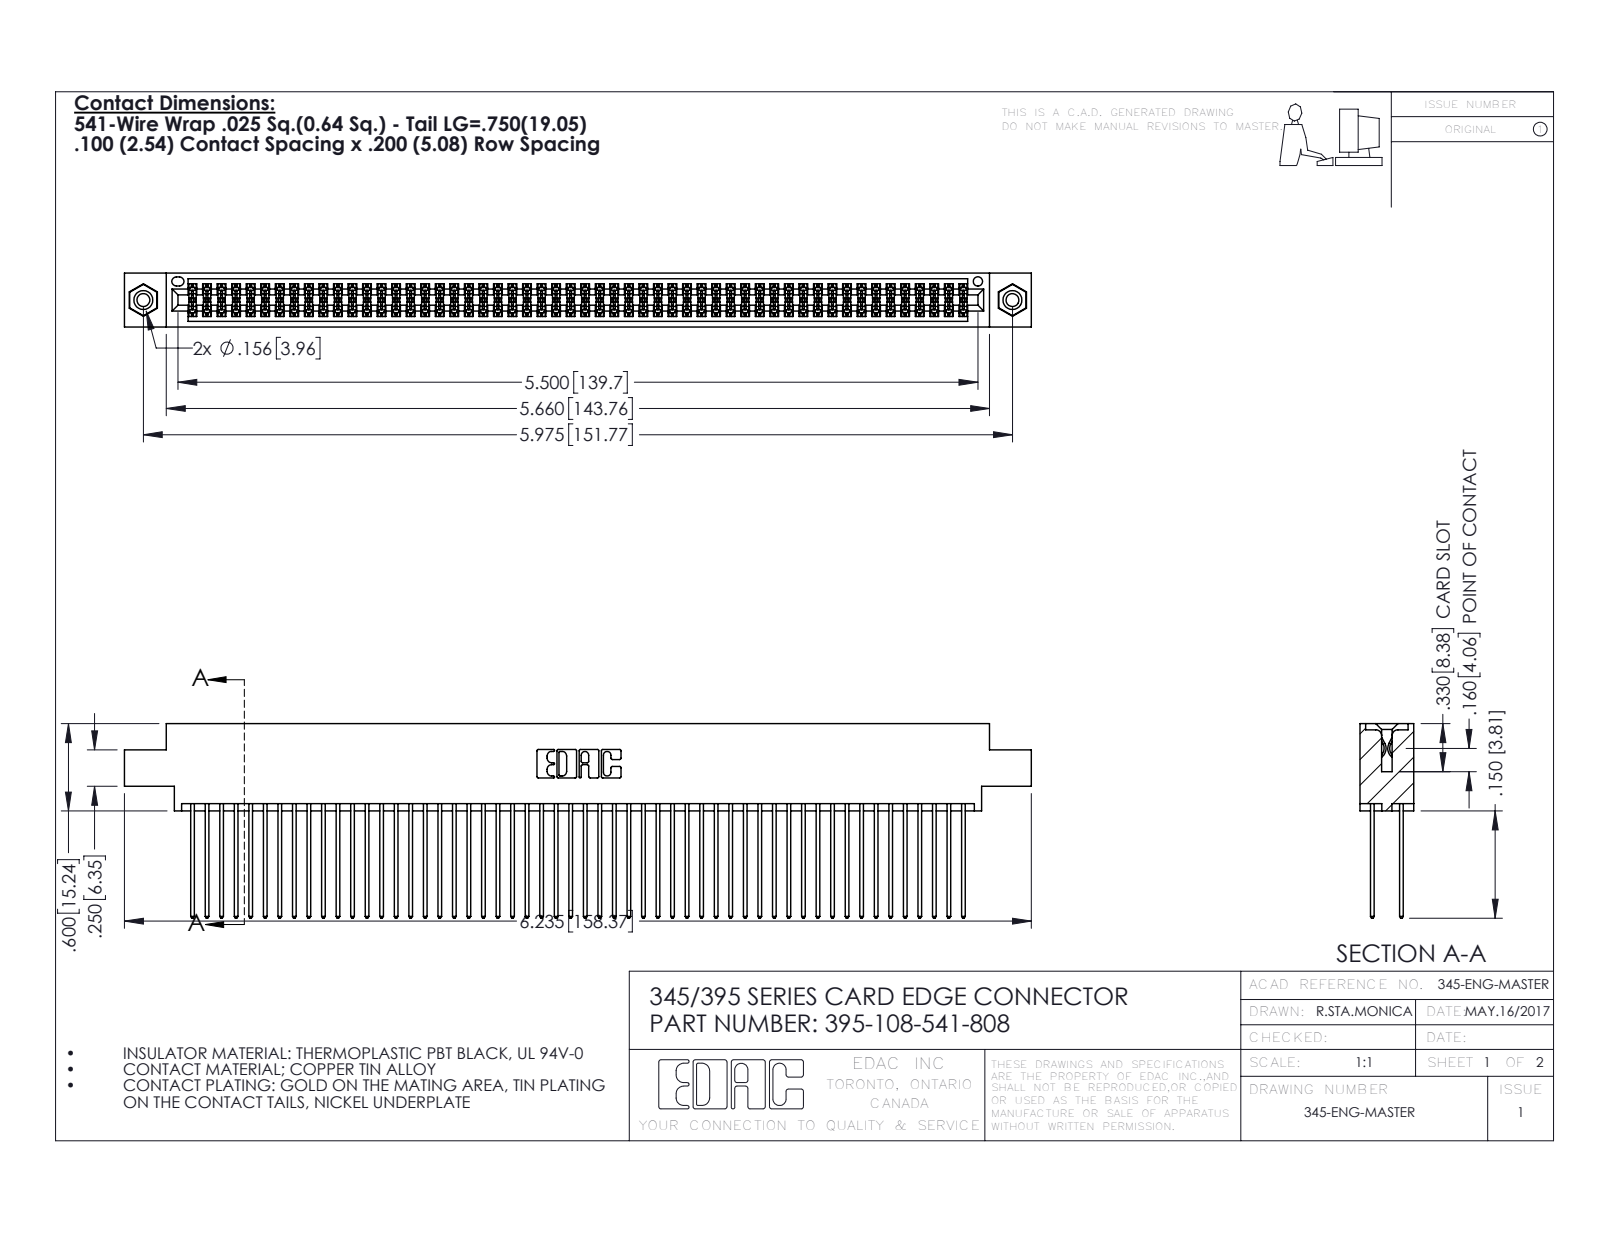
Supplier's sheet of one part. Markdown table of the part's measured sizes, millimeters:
| quantity | value |
| --- | --- |
| part name | 345-292-001_345-293-141; 345 Part_0.170 Offset - 0.156 Dia-TI; 345-250-001_345-250-003-102; 395-108-541-808 |
| STEP written by | SolidWorks 2016 (CONFIG_CONTROL_DESIGN) |
| units | millimeters |
| bodies | 111 solids, 5590 faces (3680 planar, 1894 cylindrical, 16 other) |
| overall size | 158.4 × 34 × 9.4 |
| volume | 16 000 mm³ |
| surface area | 26 950 mm² |
| round holes (diameter × count) | 2.3 × 2, 3.2 × 2, 4 × 2, 1.6 × 1 |
| round bosses / shafts (diameter × count) | 3.9 × 2 |
| partial cylindrical surfaces (radius × count) | 0.2 × 162, 0.3 × 108, 0.3 × 22, 0.2 × 6, 0.8 × 6, 0.7 × 3, 0.4 × 2, 0.5 × 2 |
| main face-to-face distances | 1.8, 7.6, 5.1, 2.5, 6.9, 0.6, 5.7, 9.4, 4.4, 3.8 |
| hole center spacings | 6.9, 145.8, 151.8 |
